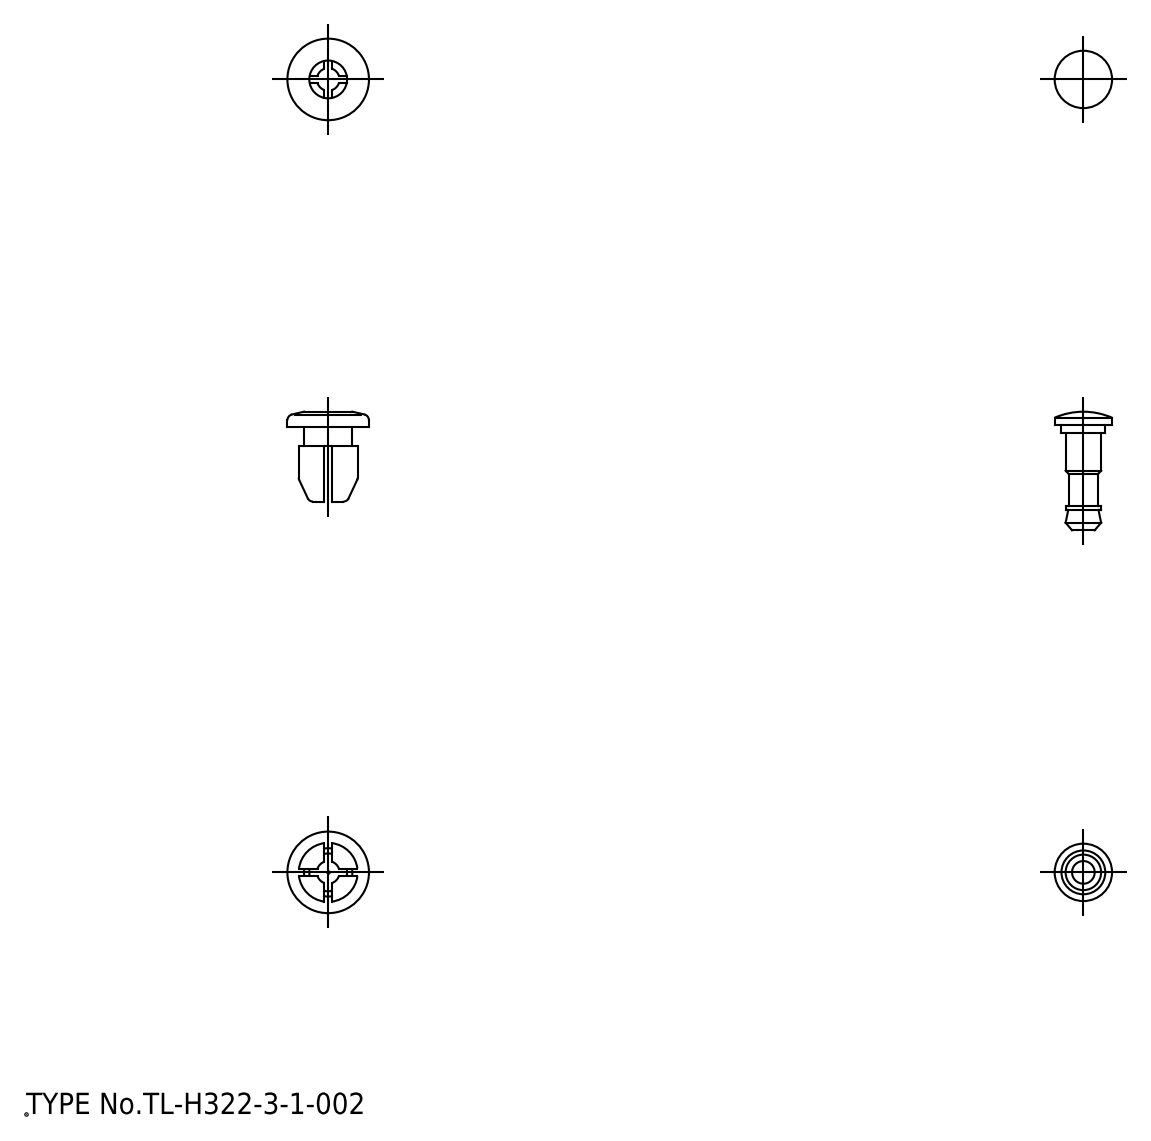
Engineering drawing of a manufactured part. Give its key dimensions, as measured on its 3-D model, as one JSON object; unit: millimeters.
{"part_name": "grommet; plunger", "step_written_by": "spGate 18.9.1 (****-****-****-****) (AUTOMOTIVE_DESIGN)", "units": "millimeters", "bodies": {"solids": 2, "faces": 79, "planar": 27, "cylindrical": 24, "other": 28}, "overall_size": [17.7, 10.8, 10.8], "volume_mm3": 586, "surface_area_mm2": 941, "round_holes": [[5, 1]], "round_bosses_or_shafts": [[10.8, 1], [7.8, 1], [7.6, 1], [6.4, 1], [5.8, 1], [4.7, 1], [3.8, 1]], "partial_cylinders_radius": [[1.5, 1]], "face_to_face_distances": [1, 6, 2, 2.5, 8.5, 4.5, 4, 9.9, 4.7, 2.7]}
